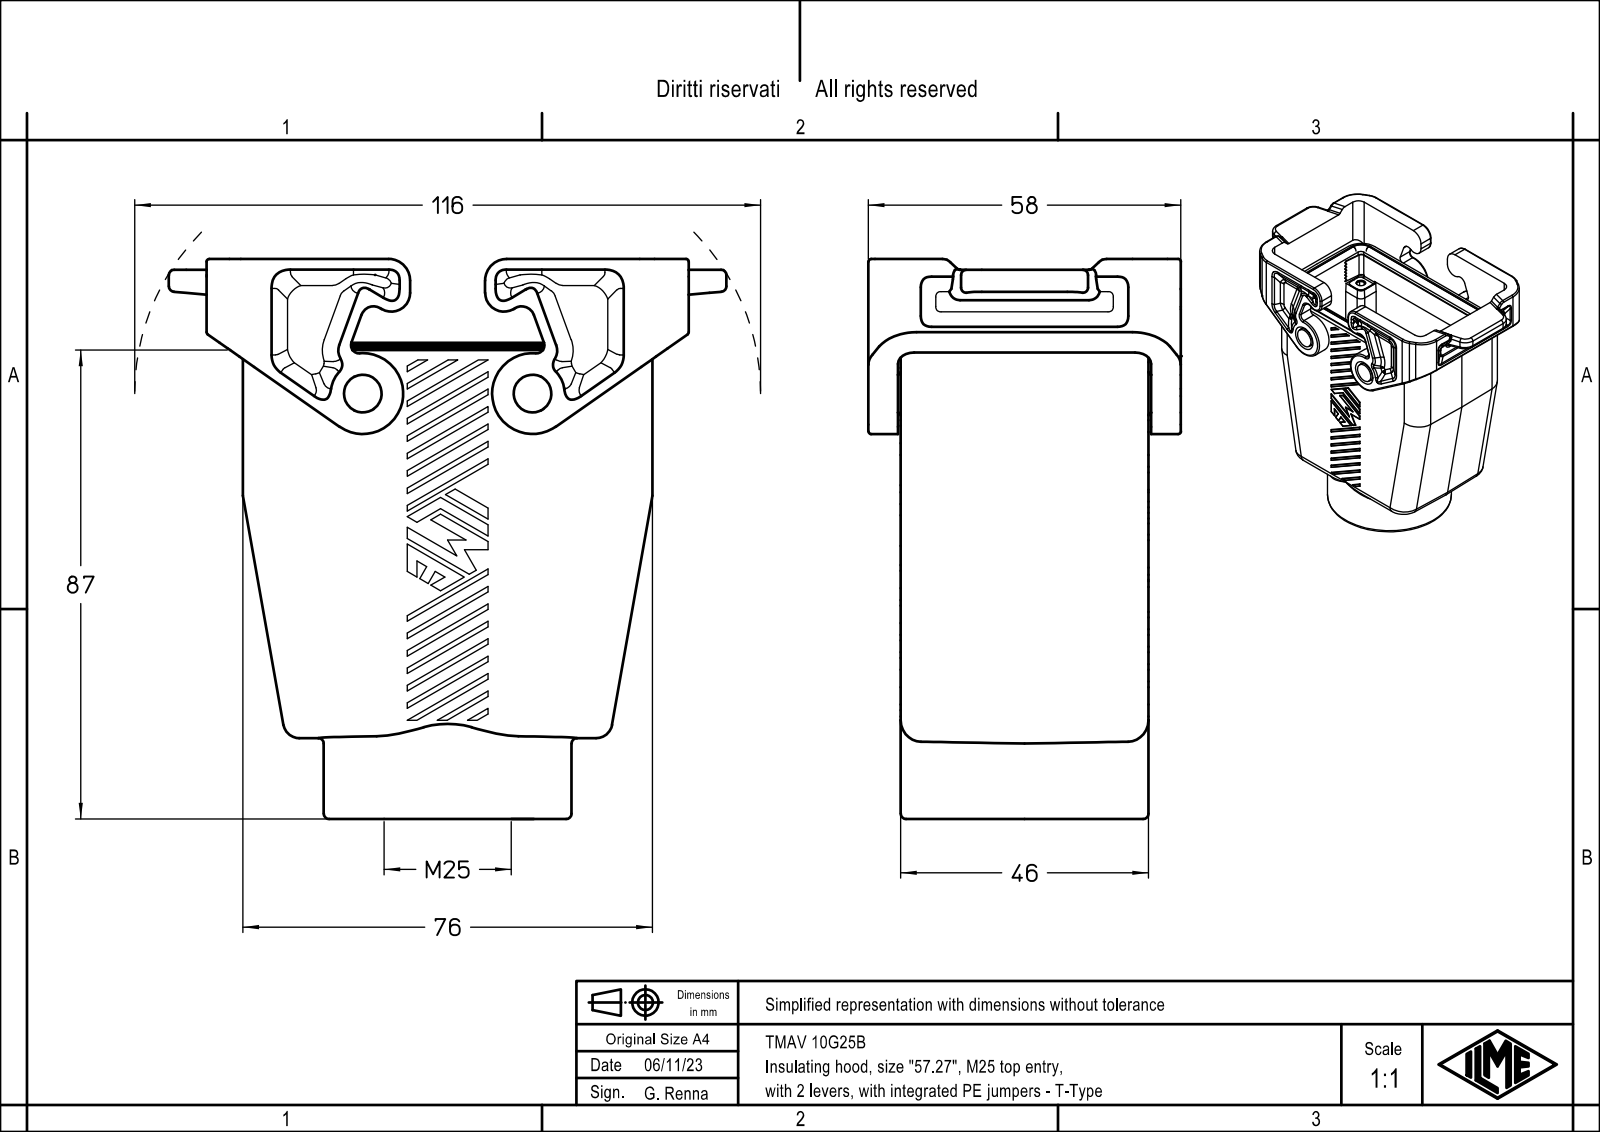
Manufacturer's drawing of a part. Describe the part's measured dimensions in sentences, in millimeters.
The part is named "TMAV 10G25B". Its 3-D file was written by "Creo Elements/Direct Modeling 20.1B 02-Apr-2019 (C) Parametric Technology GmbH (AUTOMOTIVE_DESIGN)". It is 1 solid with 856 faces: 396 planar, 398 cylindrical and 62 other. Overall it measures 103.9 by 103.5 by 58 millimeters. Its volume is 140 081 cubic millimeters and its surface area 54 195 square millimeters. Round holes: 4 of diameter 3.5, 1 of diameter 21, 1 of diameter 23.6. Round bosses or shafts: 2 of diameter 7, 1 of diameter 46. Partial cylindrical surfaces (rounded edges, fillets, slot ends): 128 of radius 0.15, 20 of radius 2, 20 of radius 3, 18 of radius 1.5, 16 of radius 1, 12 of radius 1.3, 8 of radius 6, 8 of radius 7. The main face-to-face distances are 5.4, 40.6, 46, 35.2, 0.5, 5.9, 41.1, 46.5, 5.5, 52.5. The hole center spacings are 31.54, 27, 57, 63.07.
